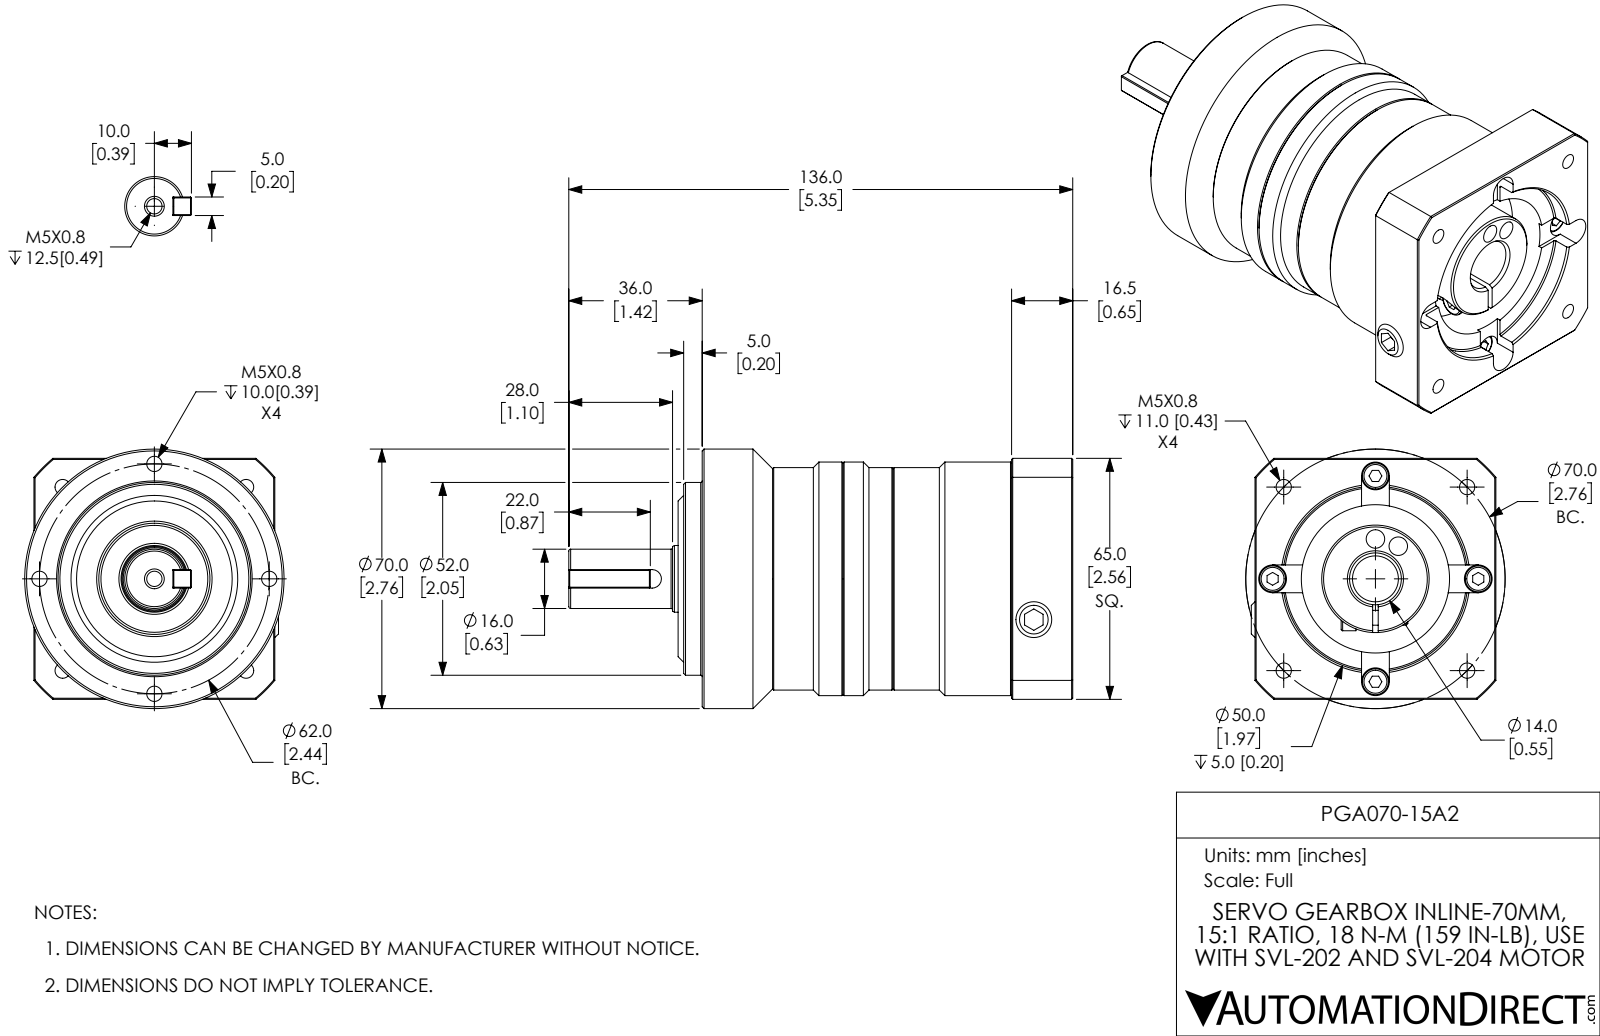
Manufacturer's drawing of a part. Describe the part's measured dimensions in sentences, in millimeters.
The part is named "PGA070-15A2". Its 3-D file was written by "SolidWorks 2019 (CONFIG_CONTROL_DESIGN)". It is 1 solid with 324 faces: 127 planar, 87 cylindrical and 110 other. Overall it measures 136 by 70 by 70 millimeters. Its volume is 323 476 cubic millimeters and its surface area 42 114 square millimeters. Round holes: 9 of diameter 4.13, 4 of diameter 7.5, 2 of diameter 5, 1 of diameter 4.5, 1 of diameter 8, 1 of diameter 14, 1 of diameter 29, 1 of diameter 40, 1 of diameter 50. Round bosses or shafts: 5 of diameter 7, 1 of diameter 70, 1 of diameter 63, 1 of diameter 60, 1 of diameter 52, 1 of diameter 18, 1 of diameter 16, 1 of diameter 4. Partial cylindrical surfaces (rounded edges, fillets, slot ends): 1 of radius 1.62, 1 of radius 2.5, 1 of radius 4, 1 of radius 42.5. The main face-to-face distances are 100, 65, 16.5, 83.5, 5, 11.5, 6.5, 106.5, 90, 1.5. The hole center spacings are 24.93, 25.53, 41.61, 58.04, 61, 3.25, 27.75, 31.
